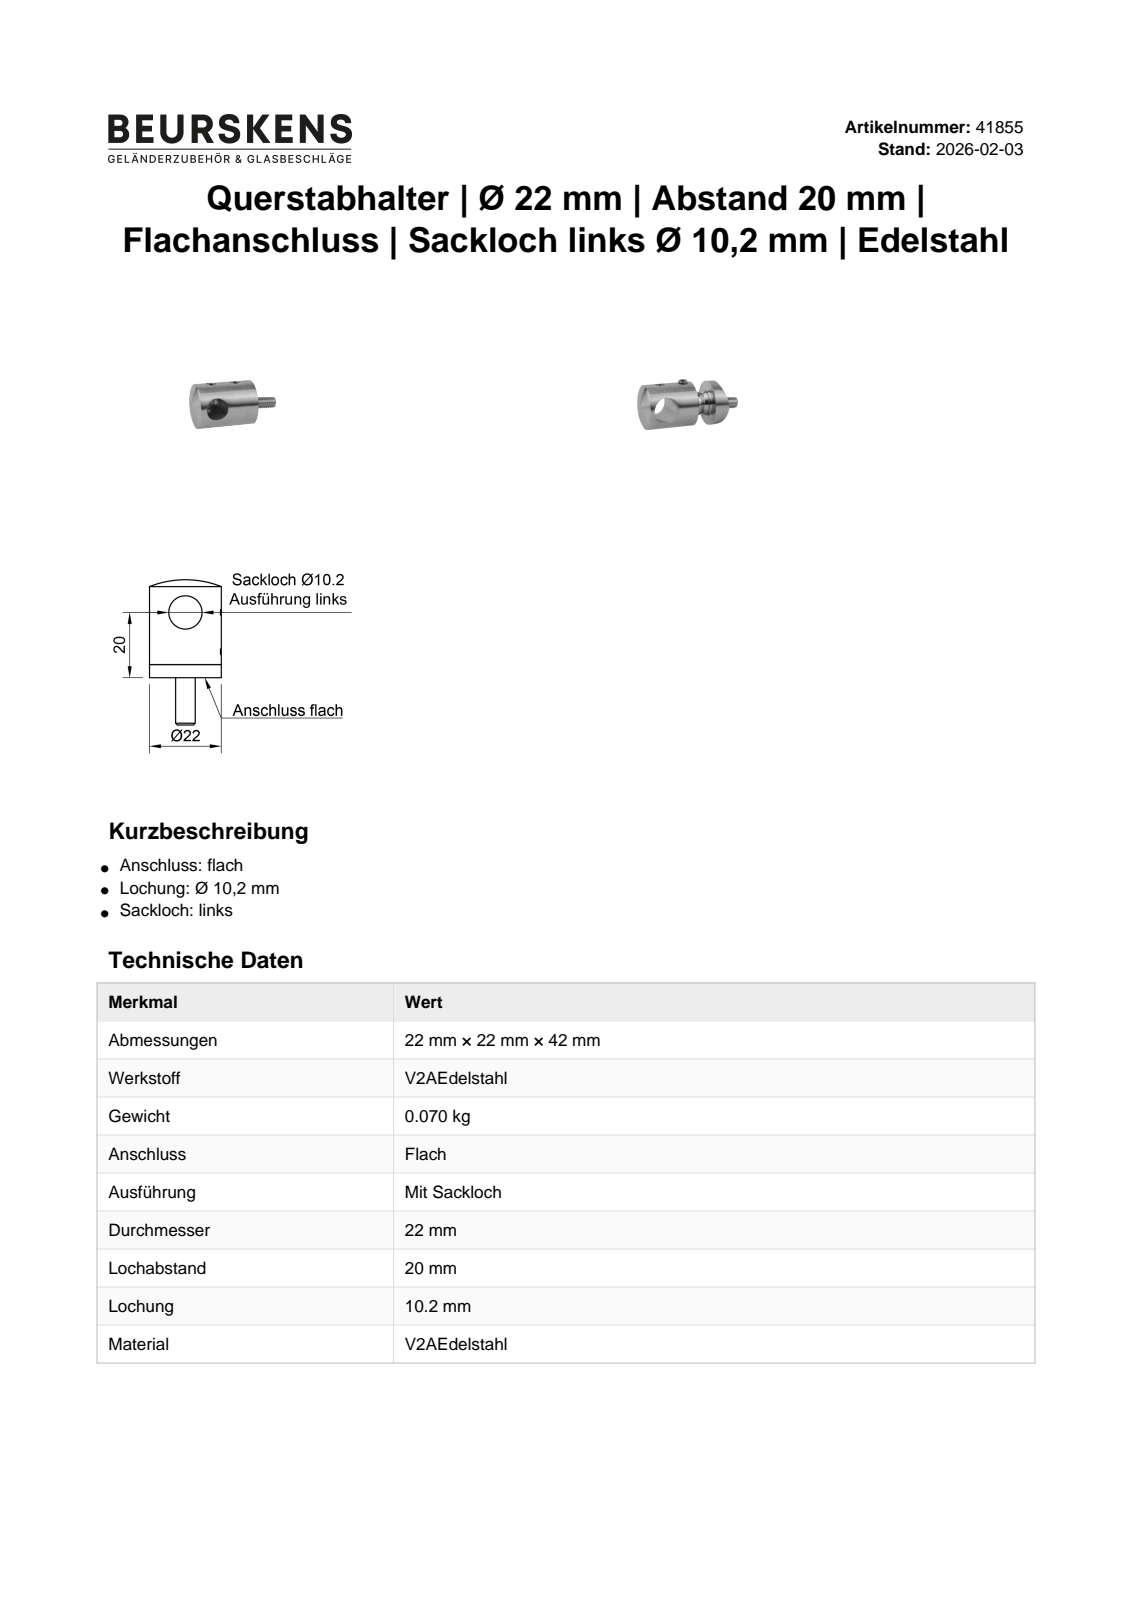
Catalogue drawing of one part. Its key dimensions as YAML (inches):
part_name: "41855; H-22-42.4ñ; socket countersunk head screw_din_DIN 7991 - M6 x 25 --- 18.7N; socket set screw flat point_din_DIN 913 - M5 x 5-N"
step_written_by: "SolidWorks 2020 (CONFIG_CONTROL_DESIGN)"
units: inches
bodies: {solids: 5, faces: 97, planar: 39, cylindrical: 26, other: 32}
overall_size: [1.751, 0.866, 0.866]
volume: 0.576
surface_area: 8.944
round_holes:
  - {diameter: 0.157, count: 2}
  - {diameter: 0.276, count: 1}
  - {diameter: 0.402, count: 1}
  - {diameter: 0.441, count: 1}
  - {diameter: 0.551, count: 1}
round_bosses_or_shafts:
  - {diameter: 0.197, count: 2}
  - {diameter: 0.866, count: 1}
  - {diameter: 0.504, count: 1}
  - {diameter: 0.456, count: 1}
  - {diameter: 0.236, count: 1}
face_to_face_distances: [0.157, 0.079, 0.414, 0.256, 0.374, 0.335, 0.531, 0.453, 0.118, 0.236]
hole_center_spacings: [0.472]
